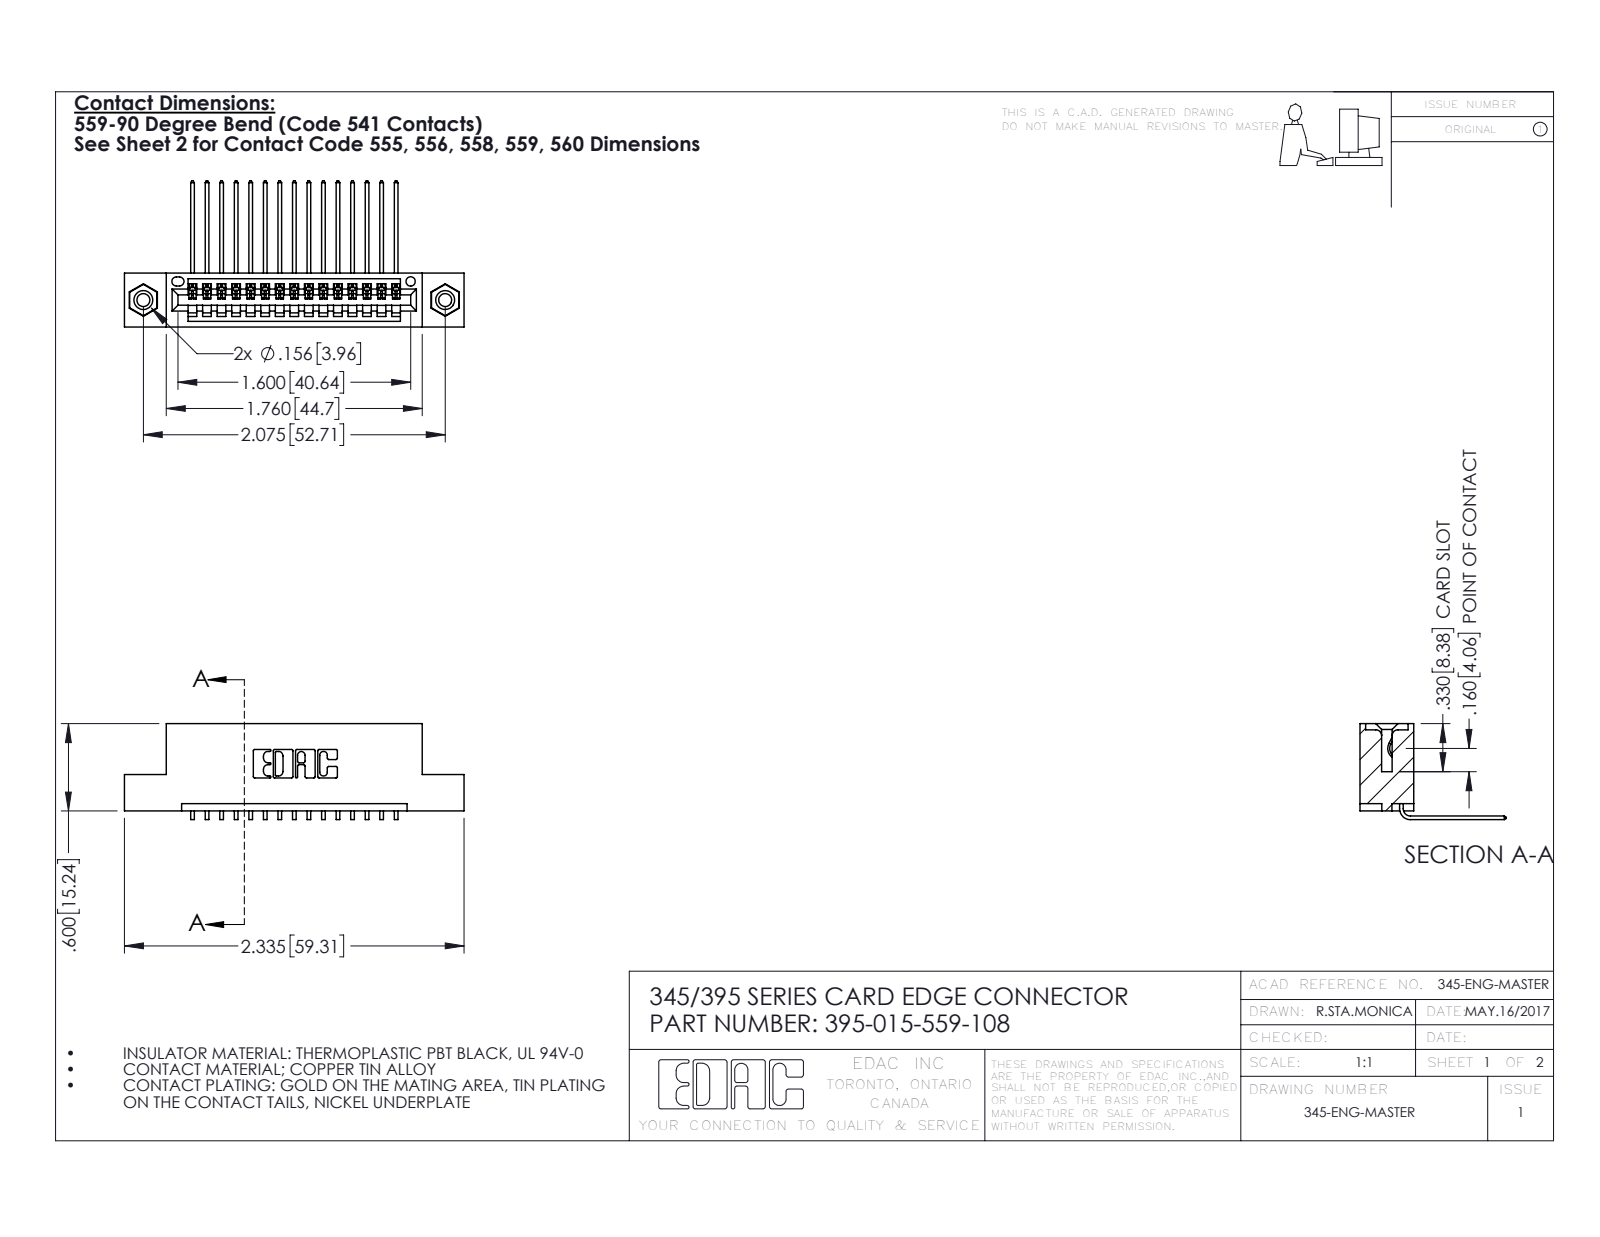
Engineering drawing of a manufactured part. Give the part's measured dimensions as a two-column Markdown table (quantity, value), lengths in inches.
| quantity | value |
| --- | --- |
| part name | 345-292-001_558 559 Tail - 1; 395-015-559-108; 345-250-001_345-250-003-102; 345 Part_Flush Mounting Lugs - 0.156 Dia-TI |
| STEP written by | SolidWorks 2016 (CONFIG_CONTROL_DESIGN) |
| units | inches |
| bodies | 18 solids, 1086 faces (742 planar, 328 cylindrical, 16 other) |
| overall size | 2.335 × 1.005 × 0.659 |
| volume | 0.333 in³ |
| surface area | 11.15 in² |
| round holes (diameter × count) | 0.089 × 2, 0.125 × 2, 0.156 × 2, 0.064 × 1 |
| round bosses / shafts (diameter × count) | 0.155 × 2 |
| partial cylindrical surfaces (radius × count) | 0.006 × 30, 0.01 × 22, 0.007 × 6, 0.031 × 6, 0.026 × 3, 0.031 × 2, 0.04 × 2, 0.014 × 1 |
| main face-to-face distances | 0.2, 0.072, 0.298, 0.37, 0.098, 0.272, 0.025, 0.1, 0.225, 0.05 |
| hole center spacings | 0.27, 1.842, 2.075 |
